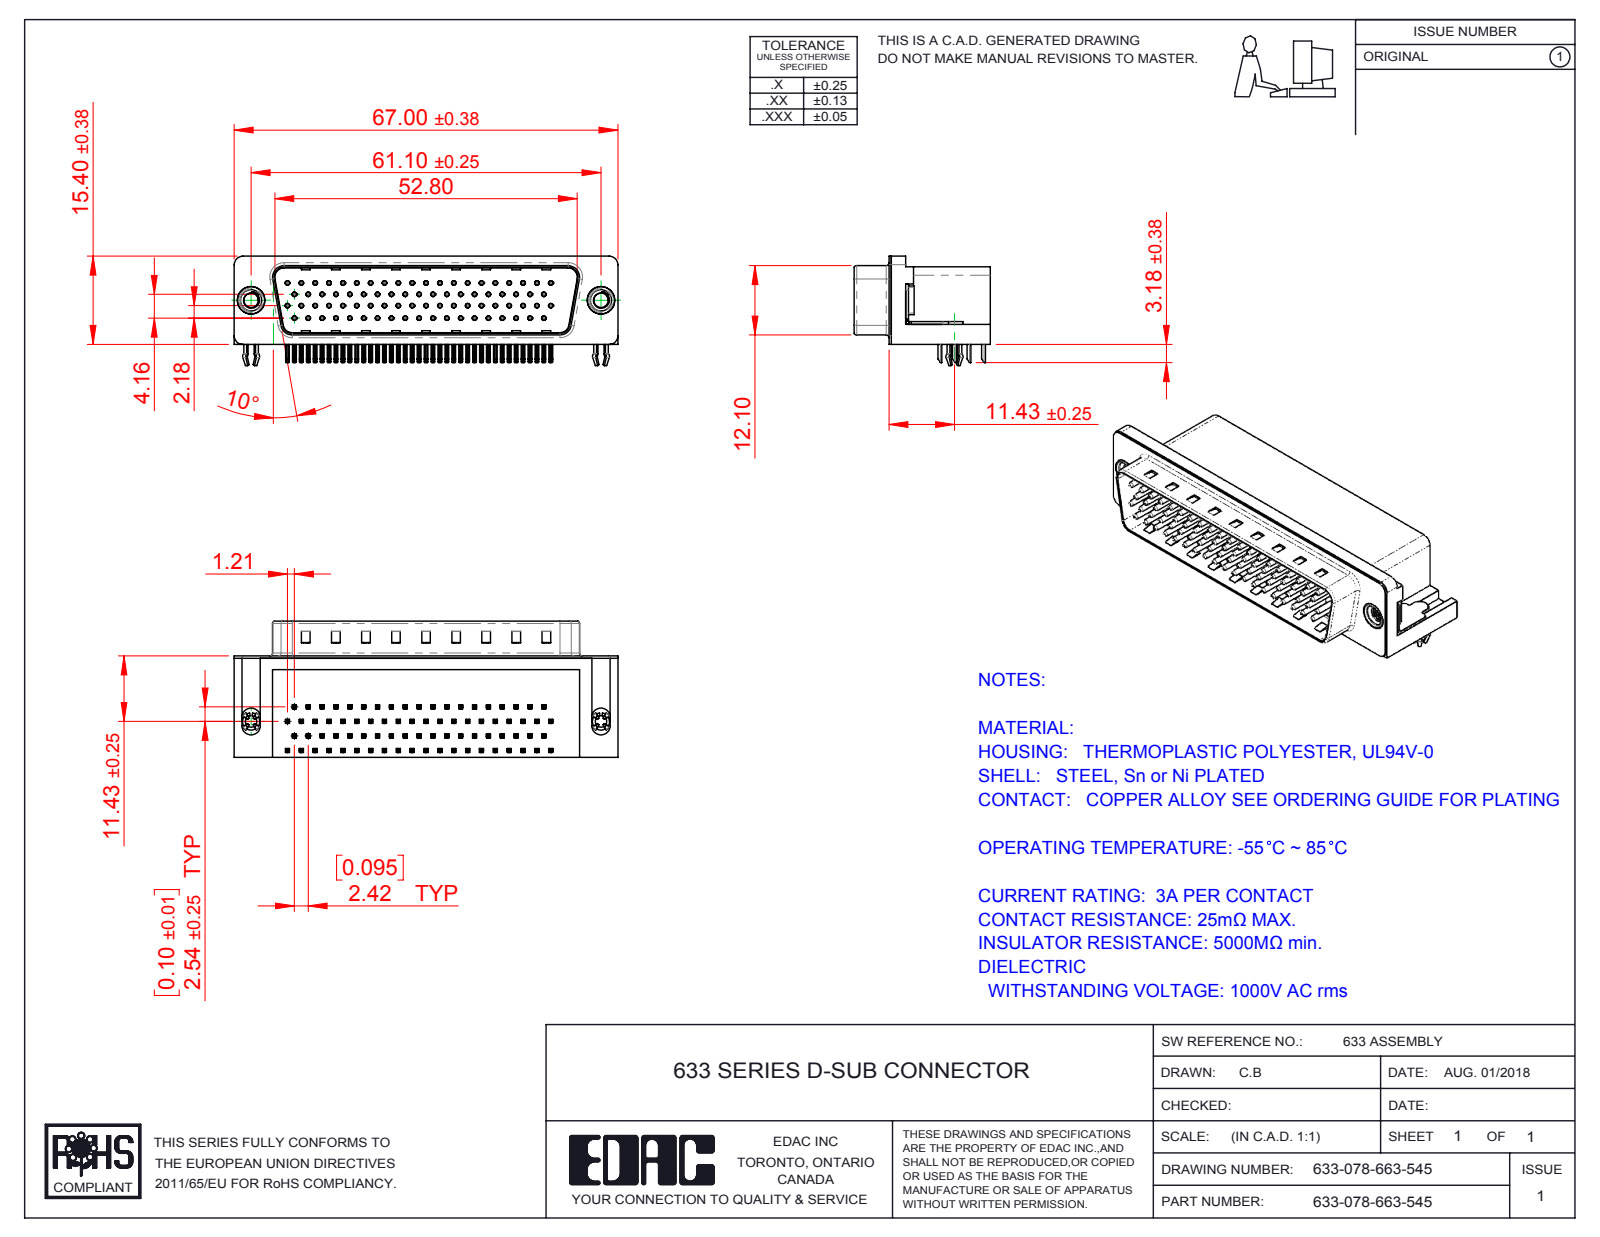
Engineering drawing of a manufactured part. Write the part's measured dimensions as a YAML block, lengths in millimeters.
part_name: "633 Shell_78 Contact; 633 Contact Middle_78 Contact; 633 4 Prong Board Lock_78 Contact; 633-078-663-545 (+5 more)"
step_written_by: "SolidWorks 2016 (CONFIG_CONTROL_DESIGN)"
units: millimeters
bodies: {solids: 84, faces: 6396, planar: 4023, cylindrical: 1788, other: 585}
overall_size: [67, 23.8, 19.1]
volume: 14617
surface_area: 16433
round_holes:
  - {diameter: 0.35, count: 78}
  - {diameter: 0.8, count: 78}
  - {diameter: 2, count: 2}
  - {diameter: 2.5, count: 2}
  - {diameter: 4, count: 2}
  - {diameter: 4.8, count: 2}
  - {diameter: 5, count: 2}
round_bosses_or_shafts:
  - {diameter: 0.75, count: 78}
  - {diameter: 4.9, count: 2}
  - {diameter: 4.75, count: 2}
  - {diameter: 3.9, count: 2}
  - {diameter: 3, count: 2}
partial_cylinders:
  - {radius: 0.25, count: 324}
  - {radius: 0.12, count: 156}
  - {radius: 1, count: 16}
  - {radius: 0.5, count: 9}
  - {radius: 1.6, count: 8}
  - {radius: 1.5, count: 6}
  - {radius: 0.45, count: 4}
  - {radius: 0.9, count: 4}
face_to_face_distances: [0.4, 13.2, 17.3, 11.7, 13.35, 2.05, 13.75, 1.65, 1.85, 11.9]
hole_center_spacings: [2.42, 4.84, 7.26, 9.68, 6.26, 7.13, 12.1, 8.62]
